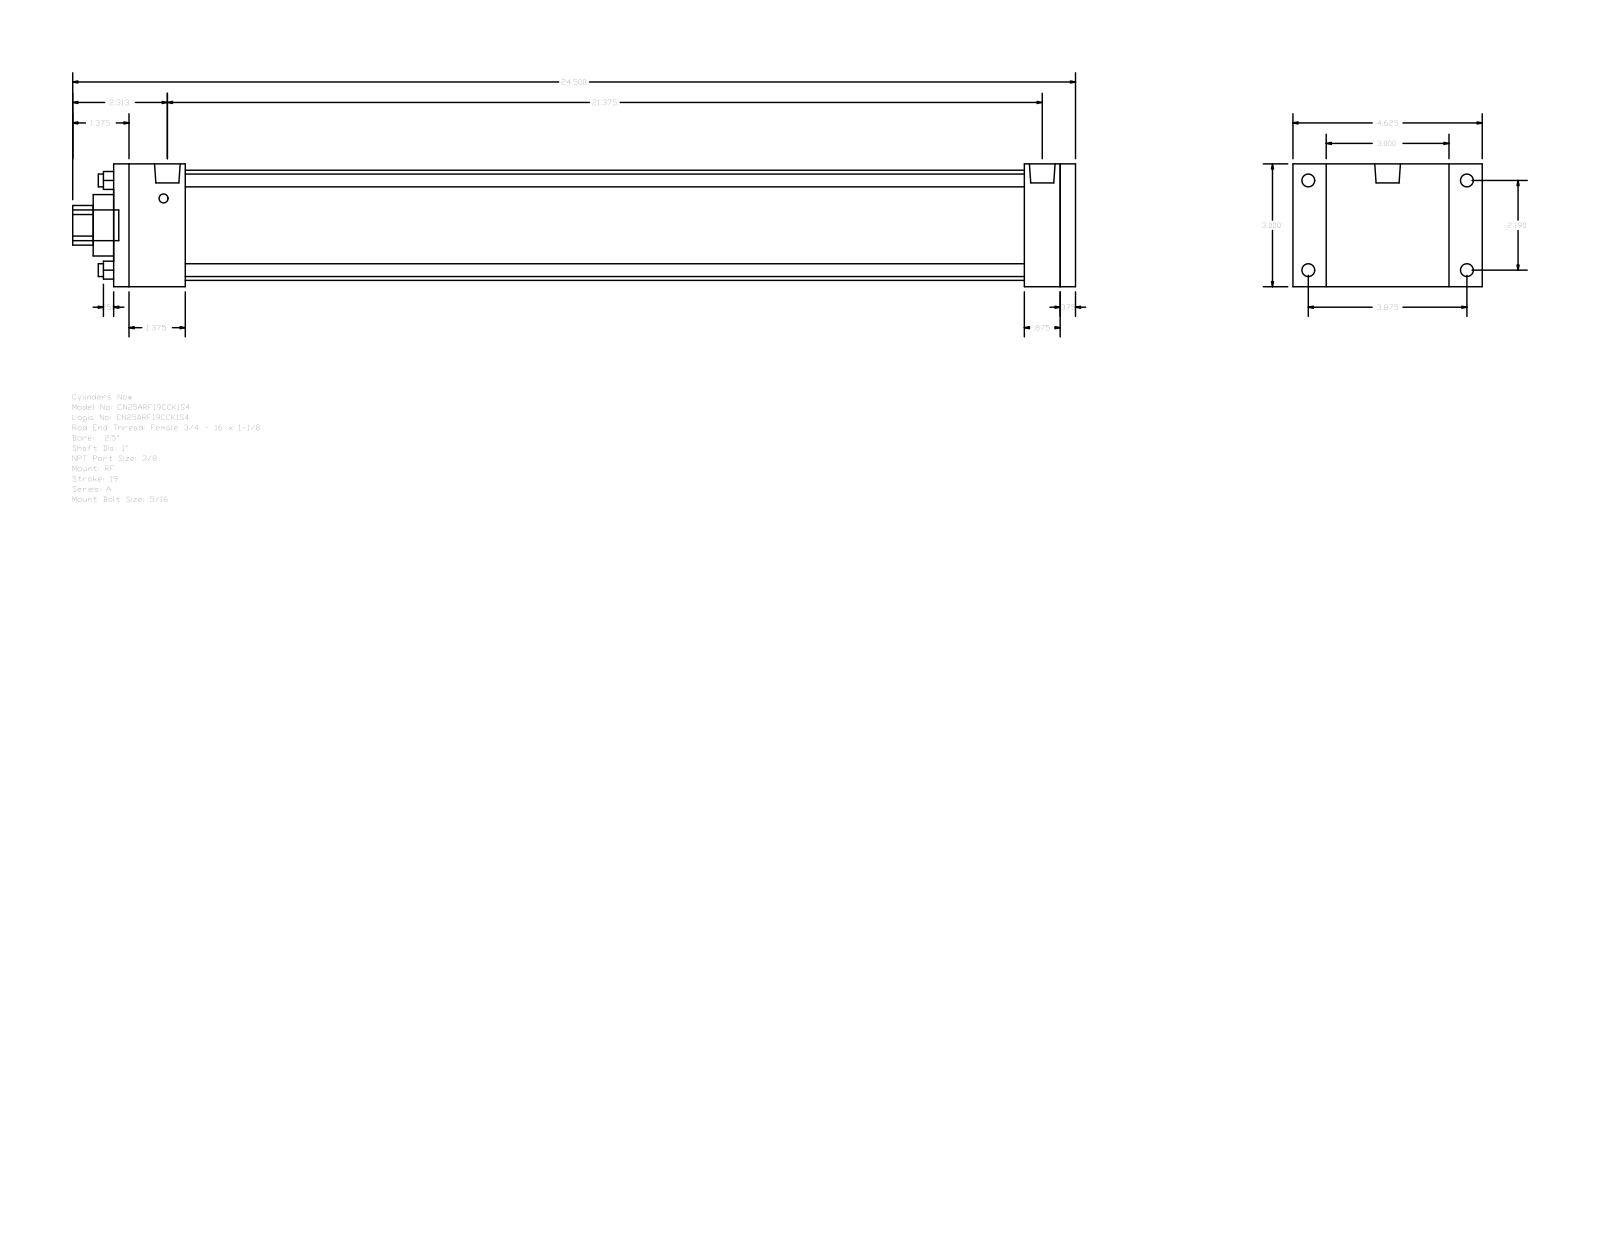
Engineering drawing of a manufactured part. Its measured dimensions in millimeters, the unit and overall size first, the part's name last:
Units: millimetres
Overall size (bounding box): 622.3 × 117.47 × 76.2
Round holes (diameter × count): ⌀7.94 ×4, ⌀25.4 ×1, ⌀38.1 ×1, ⌀68.33 ×1
Round bosses / shafts (diameter × count): ⌀7.94 ×4, ⌀5.56 ×4, ⌀15.93 ×2, ⌀19.05 ×1
Partial cylindrical surfaces — rounded edges, fillets, slot ends (radius × count): R12.29 ×1
Main face-to-face distances: 76.2, 596.9, 9.53, 587.37, 44.45, 565.15, 520.7, 542.92, 552.45, 22.22
Hole centre spacings: 39.33, 55.62, 78.66
Bodies: 0 solids, 92 faces (64 planar, 28 cylindrical, 0 other)
Part name (STEP PRODUCT): A_RF__0250_1
STEP written by: GSSL Pune (CONFIG_CONTROL_DESIGN)
